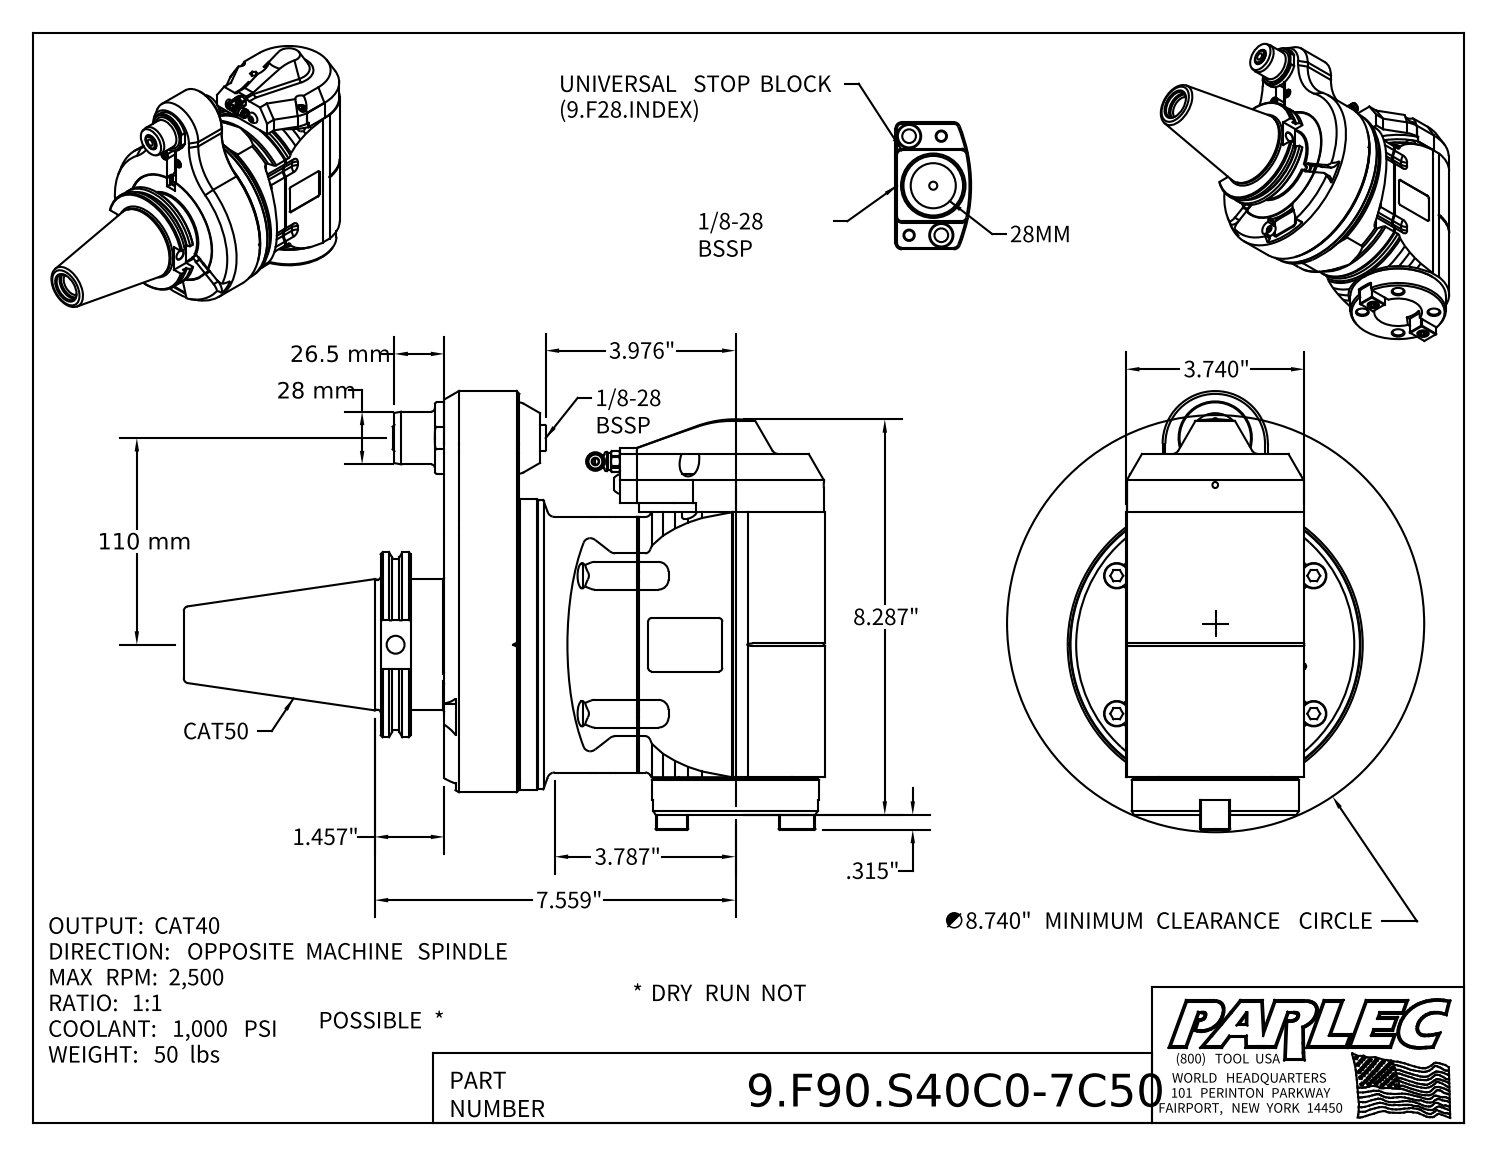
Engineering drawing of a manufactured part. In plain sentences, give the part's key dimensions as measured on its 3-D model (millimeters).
The part is named "9.F90.S40C0-7C50; 9_F90_S40B0; 9_GA3_451_2 (EVO, Type 3, Cat50, 110. 28x26.5P)". Its 3-D file was written by "Autodesk Inventor 2022 (AUTOMOTIVE_DESIGN)". It is 10 solids with 1065 faces: 484 planar, 274 cylindrical and 307 other. Overall it measures 341.1 by 233.5 by 157 millimeters. Its volume is 3 590 000 cubic millimeters and its surface area 377 400 square millimeters. Round holes: 23 of diameter 10.5, 4 of diameter 6.8, 4 of diameter 8.5, 4 of diameter 10.3, 4 of diameter 13.5, 2 of diameter 3.2, 2 of diameter 3.5, 2 of diameter 4.2, 2 of diameter 5.3, 2 of diameter 6, 2 of diameter 8, 1 of diameter 2.5. Round bosses or shafts: 6 of diameter 10, 4 of diameter 13, 4 of diameter 8, 2 of diameter 6.5, 2 of diameter 2.5, 1 of diameter 154.6, 1 of diameter 154, 1 of diameter 144. Partial cylindrical surfaces (rounded edges, fillets, slot ends): 13 of radius 2, 12 of radius 7, 10 of radius 4, 8 of radius 1, 6 of radius 3, 4 of radius 3.5, 4 of radius 5, 4 of radius 10. The main face-to-face distances are 5, 35, 30, 1, 6, 14.5, 13.5, 15.5, 19.5, 95. The hole center spacings are 64, 11.8, 57, 29.1, 89, 120.6, 128, 17.8.
